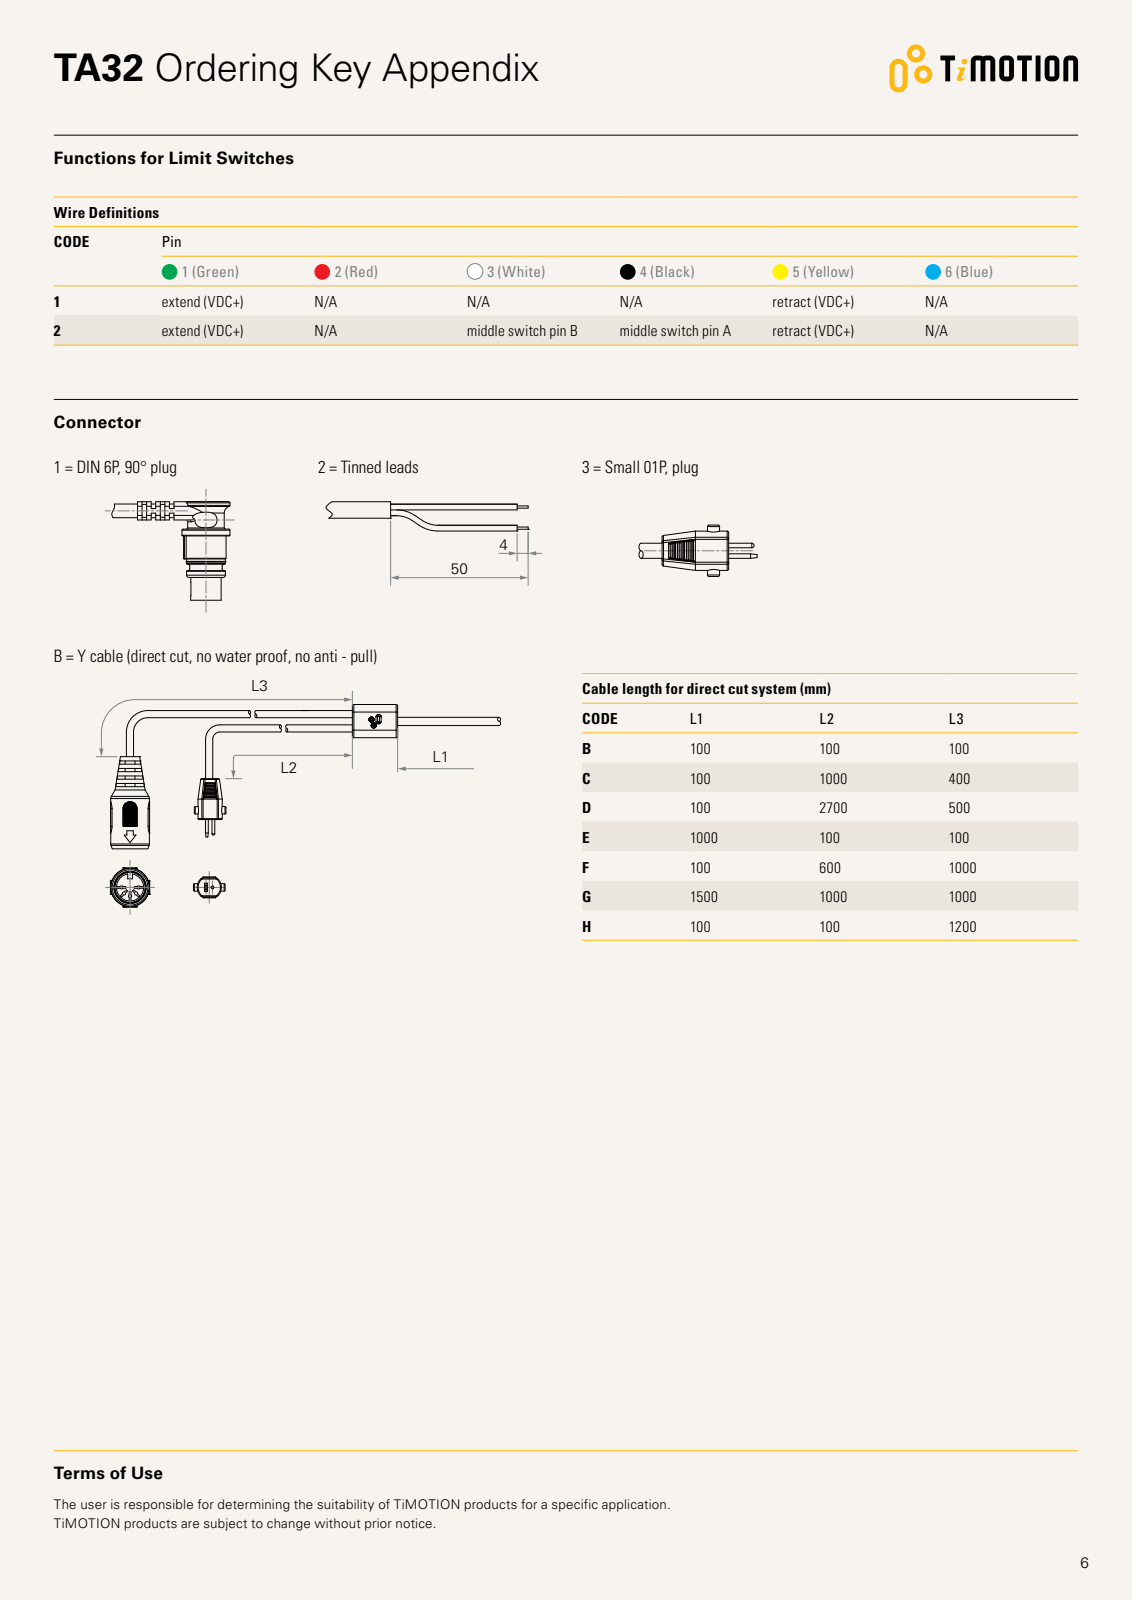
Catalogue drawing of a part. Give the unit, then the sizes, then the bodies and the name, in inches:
Units: inches
Overall size (bounding box): 6.781 × 3.45 × 2.02
Round holes (diameter × count): ⌀0.402 ×2, ⌀0.591 ×1
Round bosses / shafts (diameter × count): ⌀0.217 ×2, ⌀0.827 ×1, ⌀0.181 ×1, ⌀0.157 ×1, ⌀0.059 ×1
Partial cylindrical surfaces — rounded edges, fillets, slot ends (radius × count): R0.008 ×92, R0.012 ×12, R0.02 ×10, R0.039 ×9, R0.079 ×6, R0.063 ×4, R0.118 ×3, R0.236 ×2
Main face-to-face distances: 0.197, 0.197, 1.752, 0.26, 0.866, 0.886, 1.654, 2.617, 0.963, 3.976
Hole centre spacings: 5.669
Volume: 12.62 in³ · Surface area: 64.9 in²
Bodies: 14 solids, 575 faces (155 planar, 206 cylindrical, 214 other)
Part name (STEP PRODUCT): TA32
STEP written by: SolidWorks 2015 (CONFIG_CONTROL_DESIGN)
